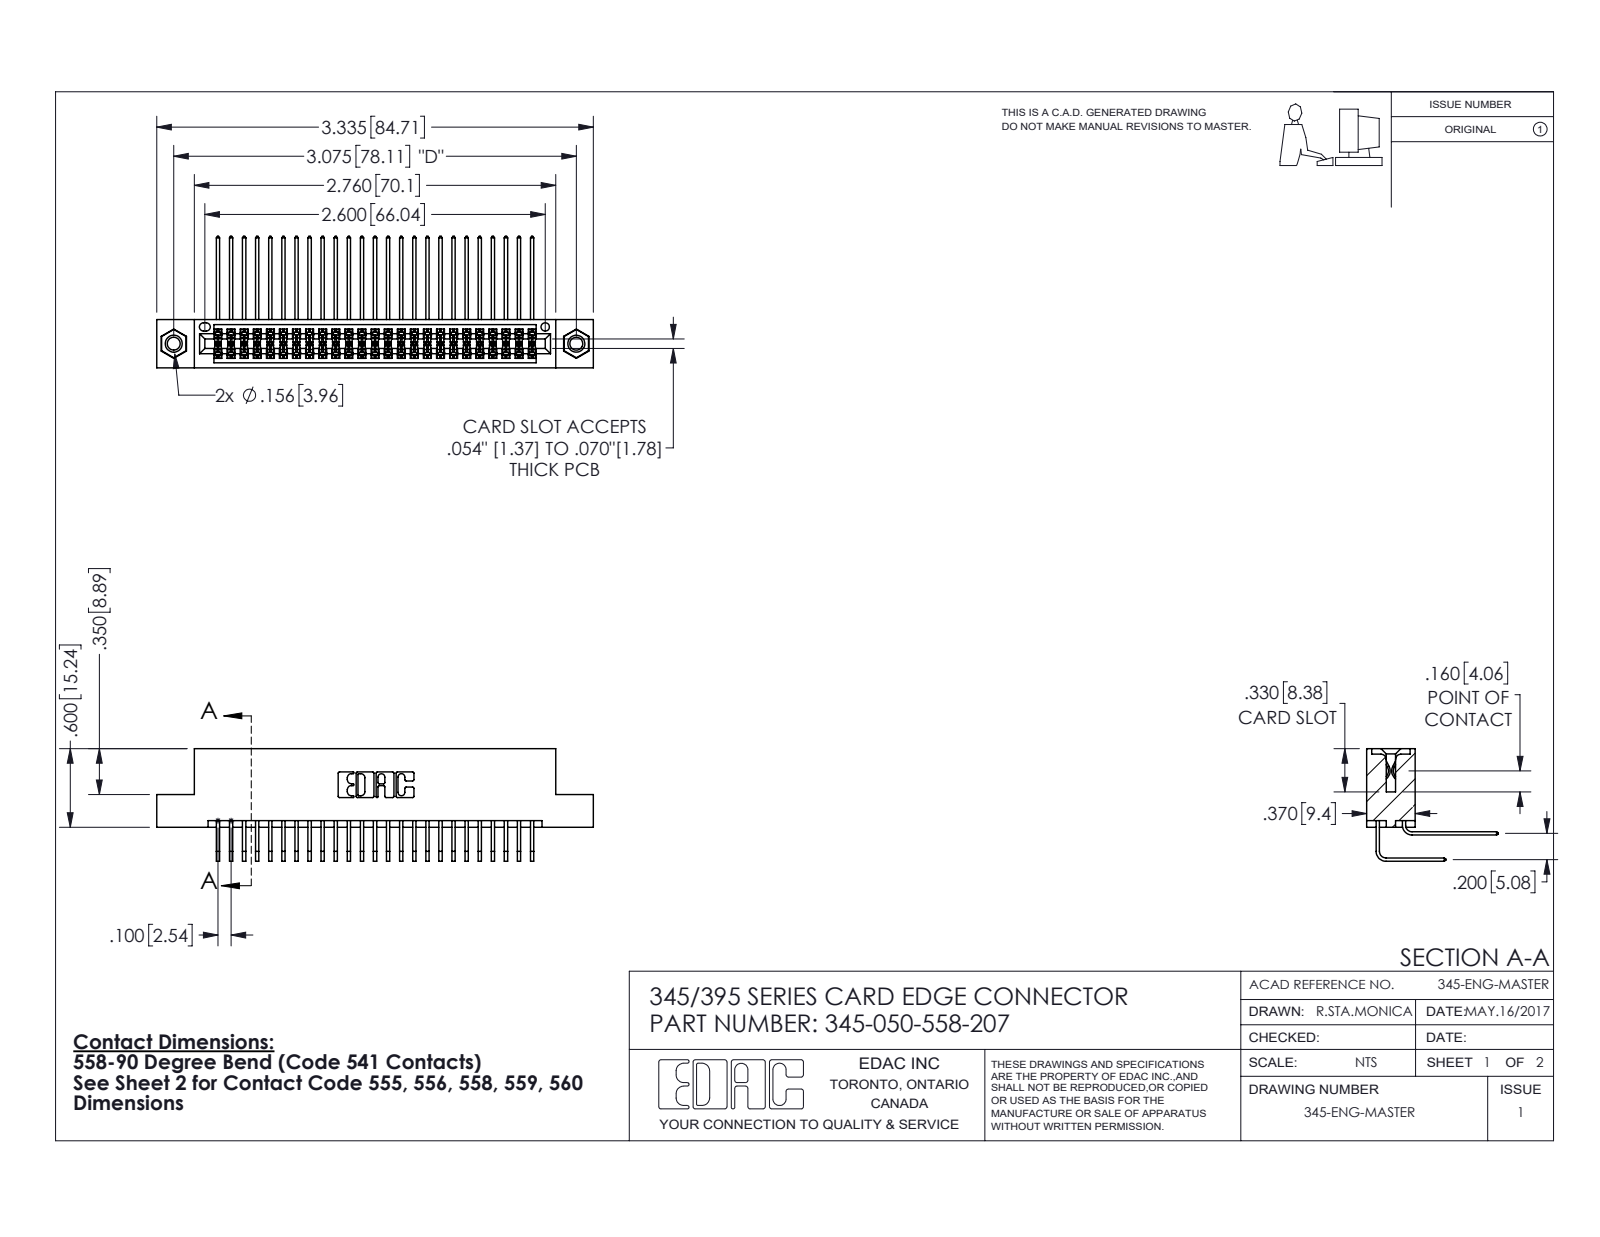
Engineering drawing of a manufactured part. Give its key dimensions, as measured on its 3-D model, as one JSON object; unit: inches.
{"part_name": "345-292-001_558 Tail - 2; 345-250-001_345-250-005-103; 345-292-001_558 559 Tail - 1; 345-050-558-207 (+1 more)", "step_written_by": "SolidWorks 2016 (CONFIG_CONTROL_DESIGN)", "units": "inches", "bodies": {"solids": 53, "faces": 2786, "planar": 1862, "cylindrical": 908, "other": 16}, "overall_size": [3.335, 1.005, 0.859], "volume_in3": 0.509, "surface_area_in2": 20.76, "round_holes": [[0.098, 2], [0.125, 2], [0.156, 2], [0.064, 1]], "round_bosses_or_shafts": [[0.155, 2]], "partial_cylinders_radius": [[0.006, 100], [0.01, 22], [0.007, 6], [0.031, 6], [0.026, 3], [0.014, 2], [0.019, 2], [0.022, 2]], "face_to_face_distances": [0.2, 0.072, 0.298, 0.37, 0.098, 0.272, 0.025, 0.225, 0.025, 0.285], "hole_center_spacings": [0.27, 2.84, 3.075]}
